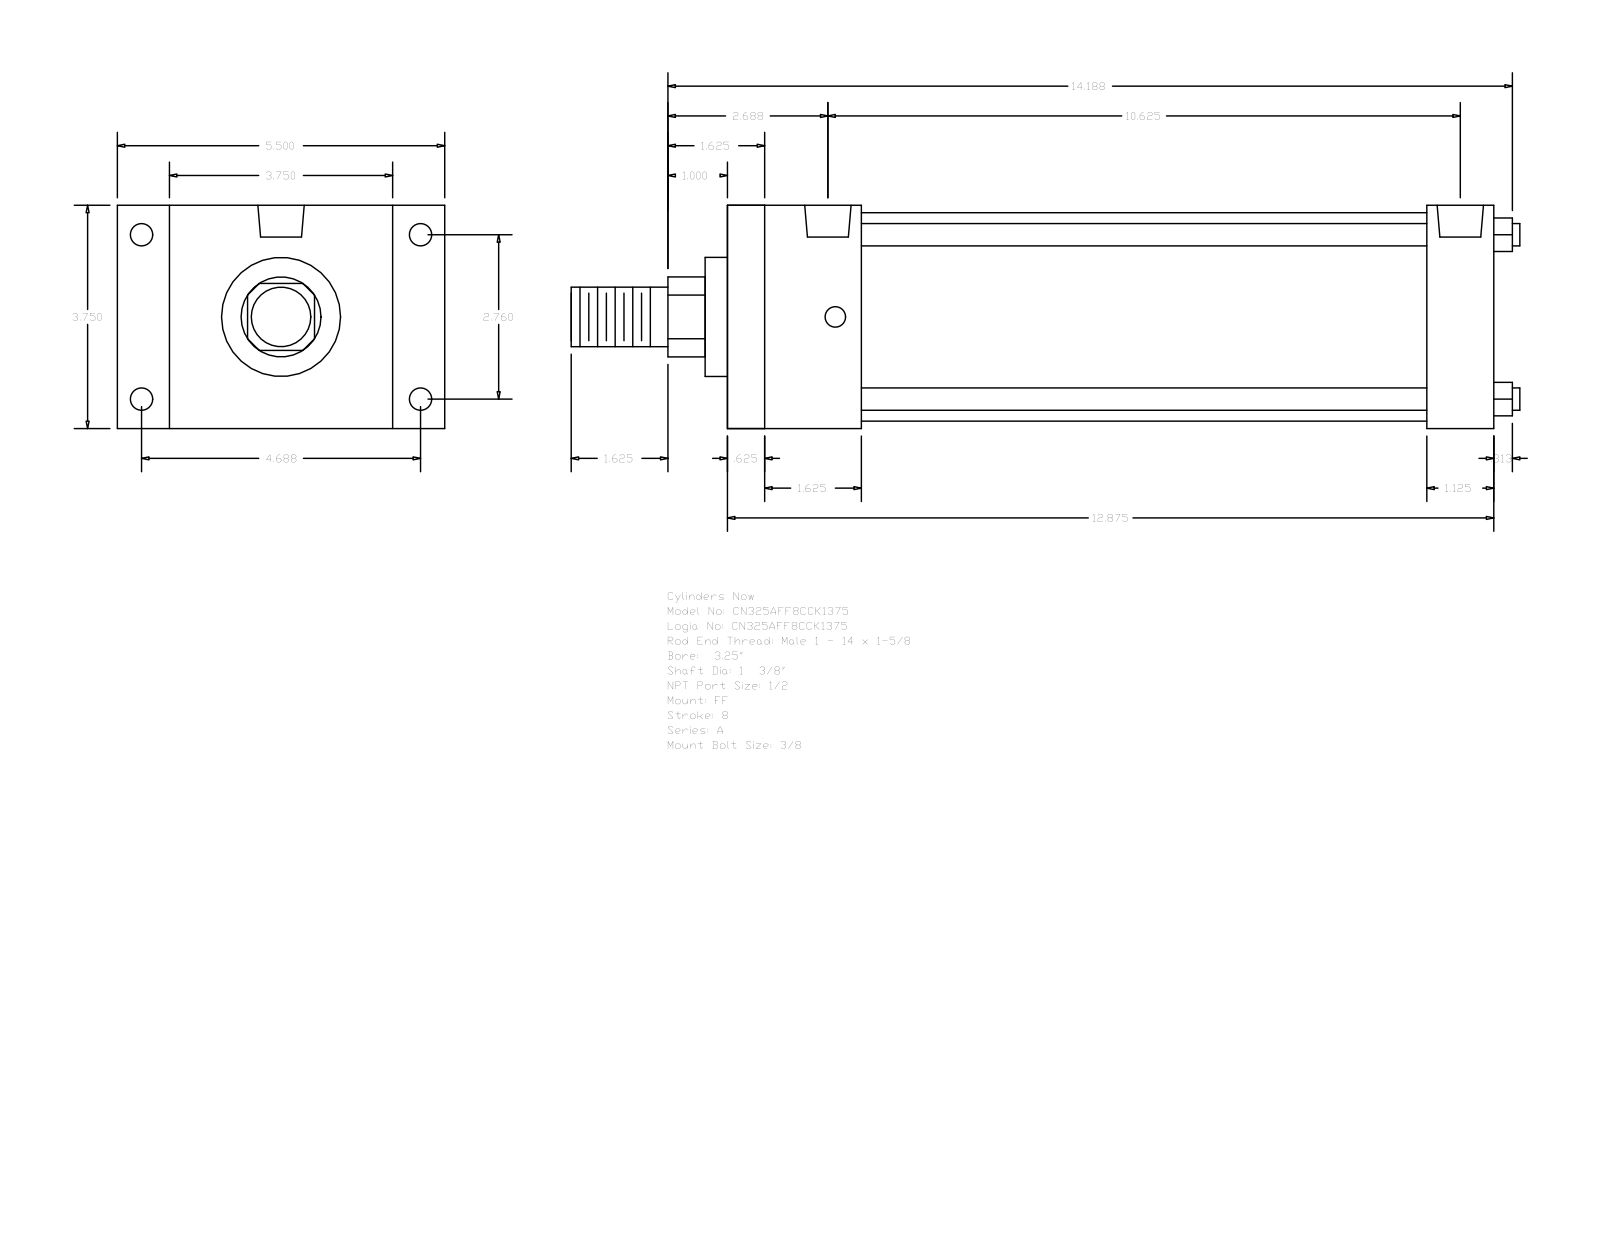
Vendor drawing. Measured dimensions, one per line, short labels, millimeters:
name: A_FF__0325_1.375
written by: GSSL Pune (CONFIG_CONTROL_DESIGN)
unit: mm
bodies: 0 solids, 92 faces (64 planar, 28 cylindrical, 0 other)
size: 404.81 × 139.7 × 95.25
holes: 4× ⌀8.73, 4× ⌀9.53, 2× ⌀19.77
bosses: 4× ⌀9.53, 1× ⌀88.9, 1× ⌀50.8, 1× ⌀34.92, 1× ⌀25.4
rounds: 1× R17.06
face distances: 95.24, 327.03, 15.87, 311.16, 57.15, 28.58, 22.23, 117.47, 298.45, 41.28
hole spacings: 3.18, 70.1, 119.06, 138.16, 263.52, 266.7, 269.88
